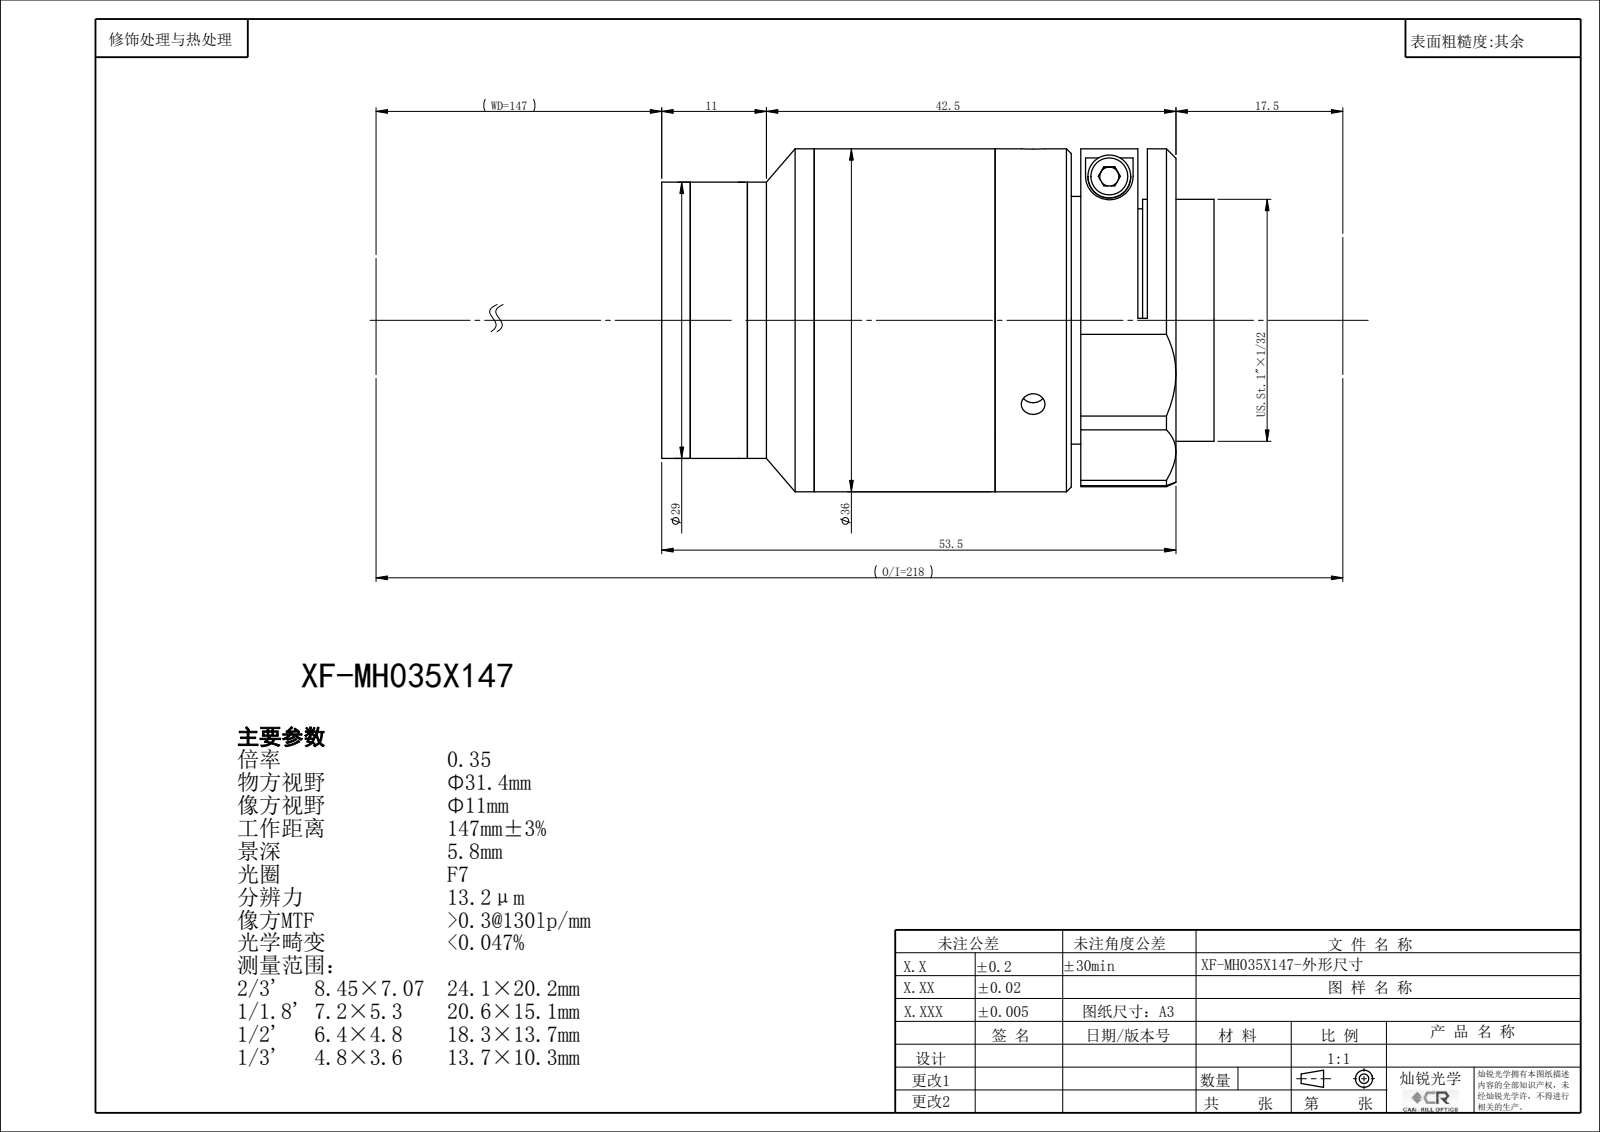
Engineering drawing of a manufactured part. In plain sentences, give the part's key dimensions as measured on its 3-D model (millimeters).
The part is named "XF-MH035X147". Its 3-D file was written by "SolidWorks 2022 (CONFIG_CONTROL_DESIGN)". It is 0 solids with 121 faces: 61 planar, 38 cylindrical and 22 other. Overall it measures 57.58 by 36.01 by 36 millimeters. Round holes: 3 of diameter 2.5, 1 of diameter 14, 1 of diameter 22.4, 1 of diameter 24, 1 of diameter 24.9, 1 of diameter 27. Round bosses or shafts: 1 of diameter 36, 1 of diameter 34, 1 of diameter 29, 1 of diameter 25.4. The main face-to-face distances are 18.55, 31.22, 49.77, 1.5, 48.27, 17.05, 12.22, 19, 36.05, 37.55.
